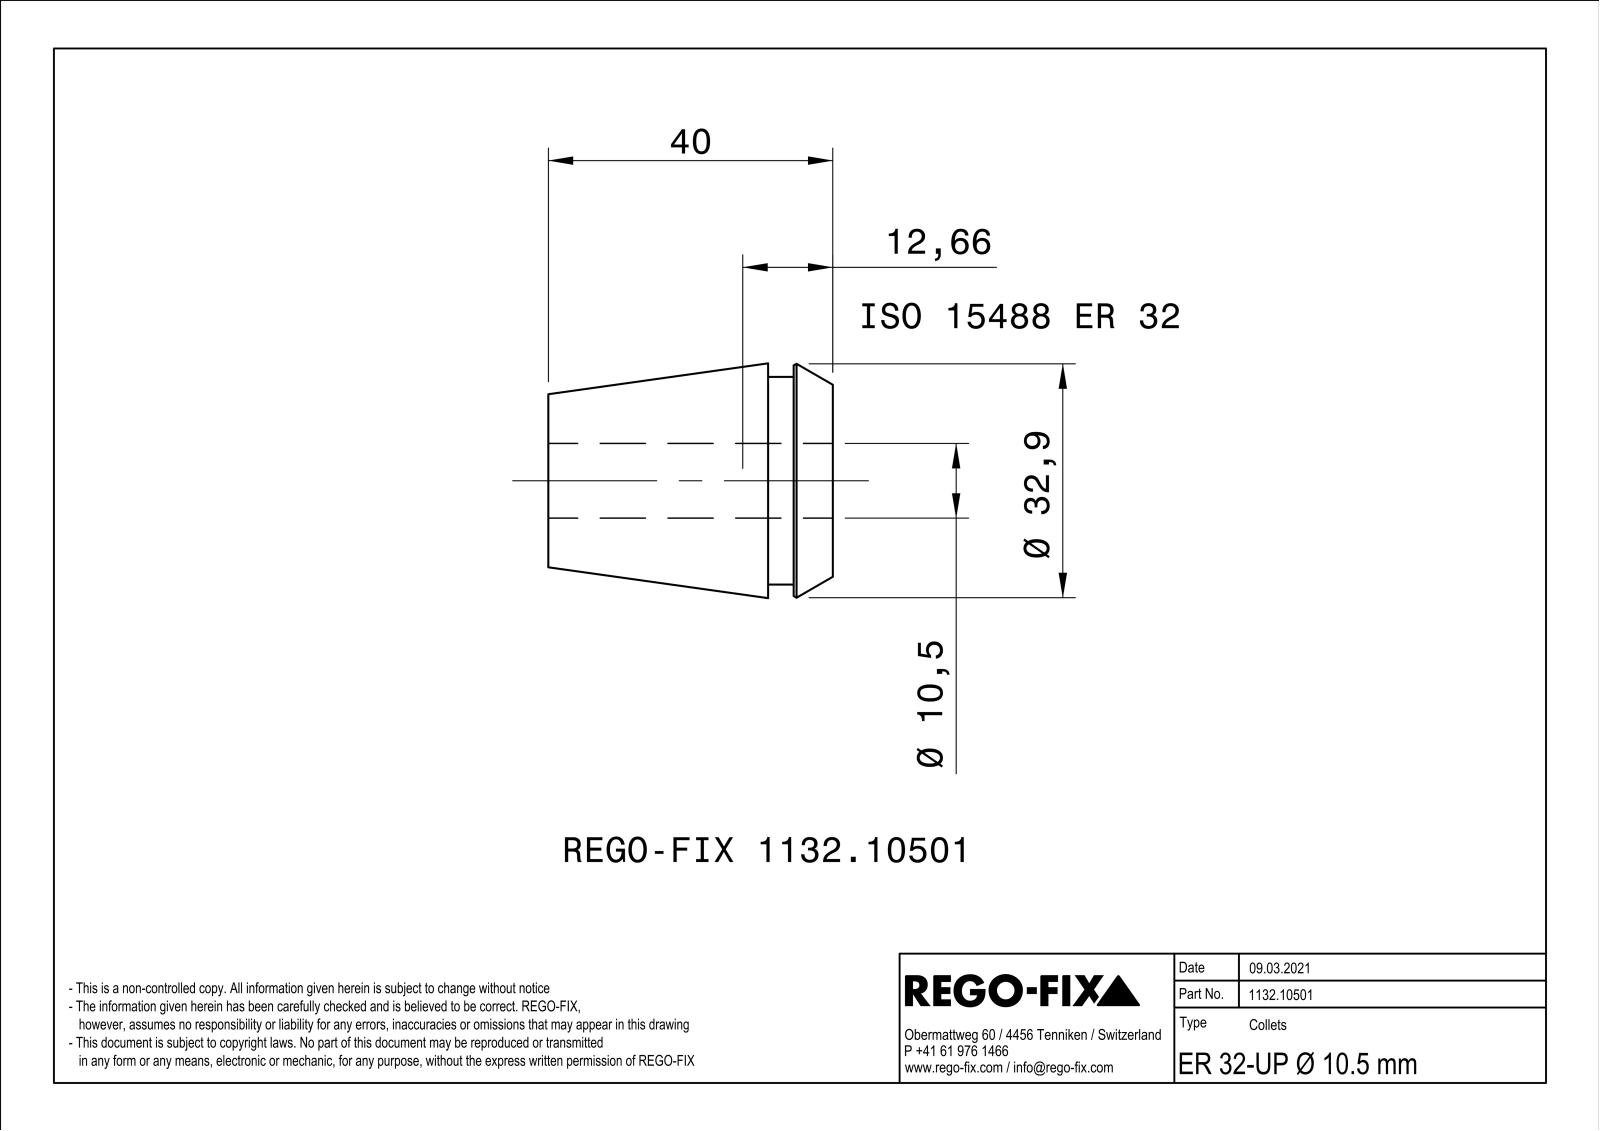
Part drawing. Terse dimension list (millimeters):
name: NOCUT
written by: SIEMENS PLM Software Solid Edge ST10 (AUTOMOTIVE_DESIGN)
unit: mm
bodies: 1 solid, 209 faces (88 planar, 41 cylindrical, 80 other)
size: 40 × 32.98 × 32.98
volume: 17 722 mm³; area: 15 535 mm²
holes: 1× ⌀10.5
bosses: 1× ⌀29.2
rounds: 20× R0.4
face distances: 1, 40, 9.1, 30.9, 5.5, 3.6, 34.5, 6, 0.5, 3.1
